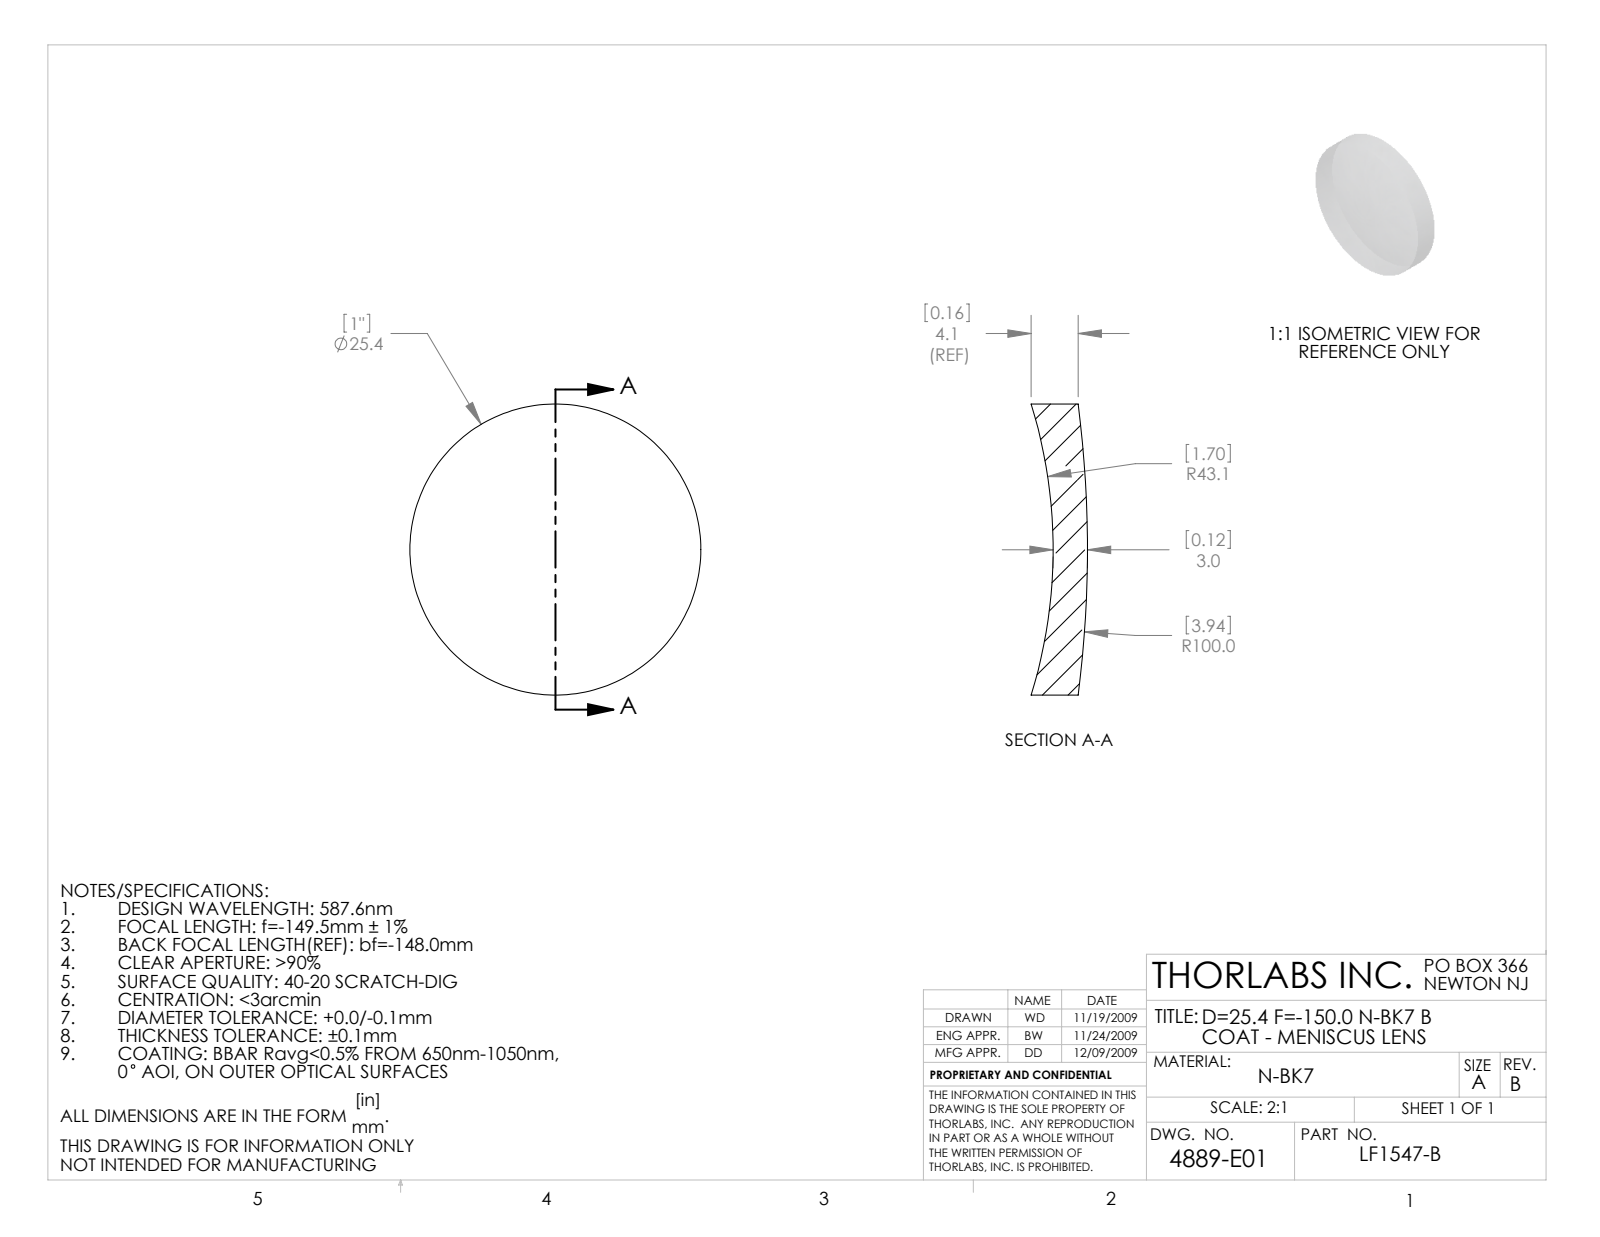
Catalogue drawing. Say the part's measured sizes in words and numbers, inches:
The part is named "4889-E0W". Its 3-D file was written by "SolidWorks 2009 (AUTOMOTIVE_DESIGN)". It is 1 solid with 6 faces: 0 planar, 2 cylindrical and 4 other. Overall it measures 1 by 1 by 0.193 inches. Its volume is 0.11 cubic inches and its surface area 2.099 square inches. Round bosses or shafts: 1 of diameter 1.
